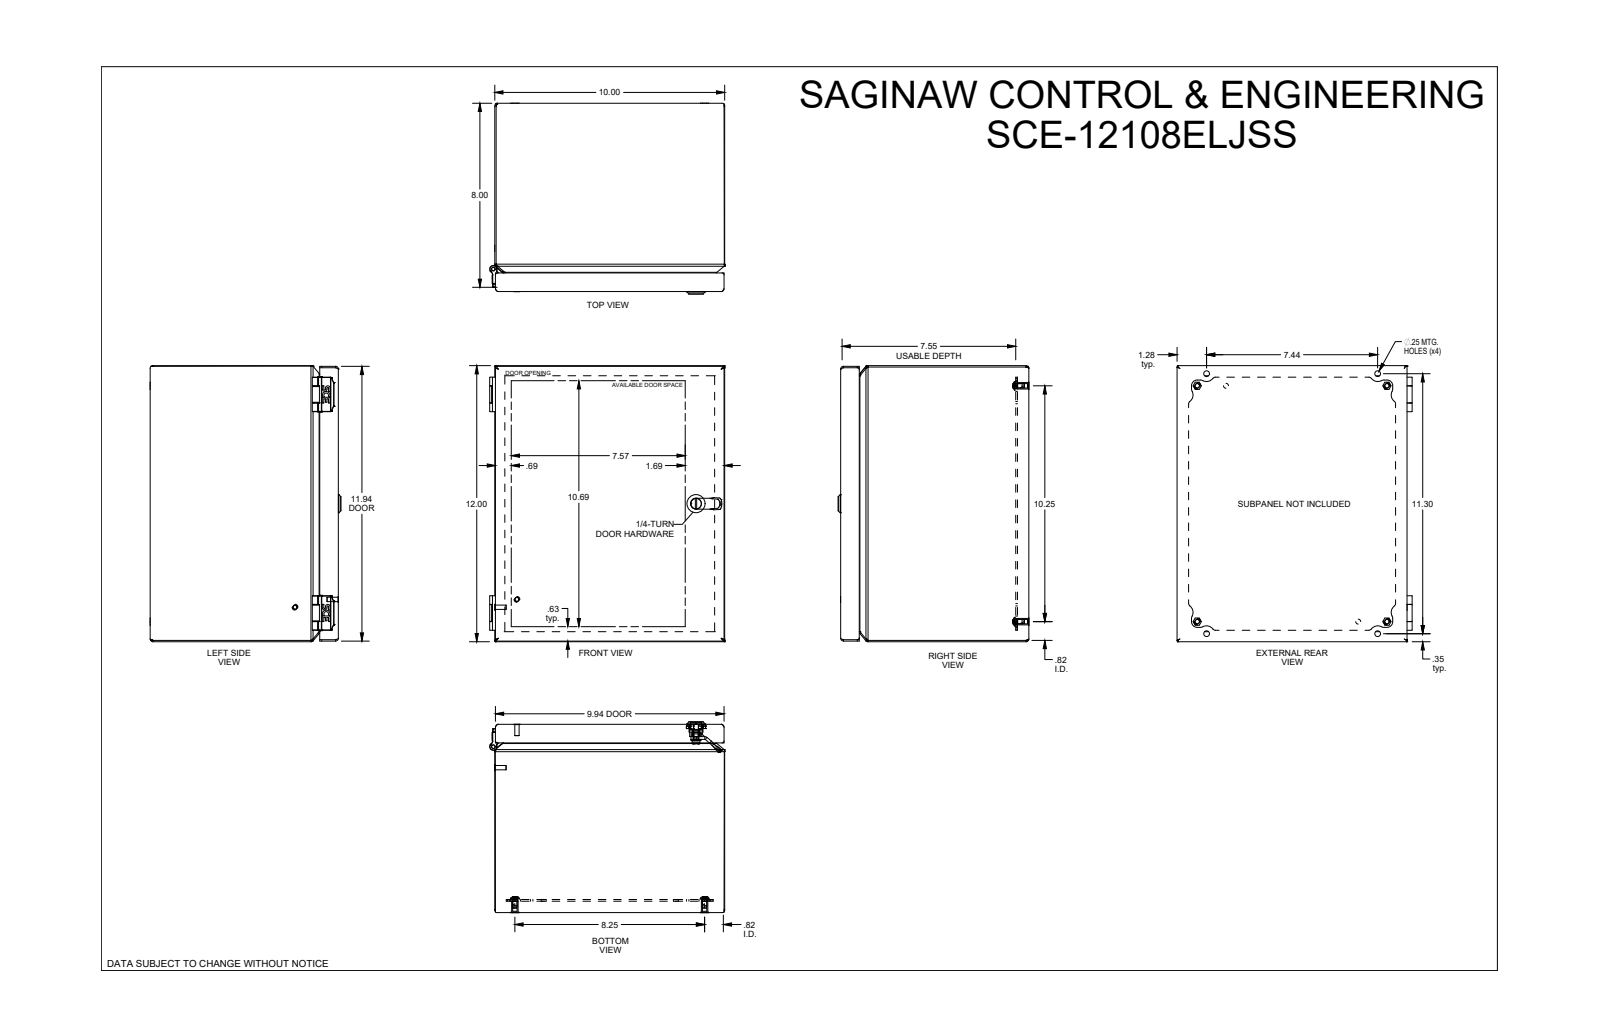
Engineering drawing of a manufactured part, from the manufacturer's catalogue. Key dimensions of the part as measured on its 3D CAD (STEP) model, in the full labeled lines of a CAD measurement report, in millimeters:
Part name (STEP PRODUCT): SCE-12108ELJ
STEP written by: SolidWorks 2019 (AUTOMOTIVE_DESIGN)
Units: millimetres
Bodies: 34 solids, 1079 faces (395 planar, 348 cylindrical, 336 other)
Overall size (bounding box): 306.3 × 259.6 × 210.7
Volume: 789 700 mm³ · Surface area: 985 200 mm²
Round holes (diameter × count): ⌀4.3 ×4, ⌀4.8 ×4, ⌀6.4 ×4, ⌀7.2 ×4, ⌀0.5 ×2, ⌀2.5 ×2, ⌀5.5 ×2, ⌀6.8 ×2, ⌀4 ×1, ⌀5 ×1, ⌀5.1 ×1, ⌀6.1 ×1
Round bosses / shafts (diameter × count): ⌀4.8 ×6, ⌀12.2 ×4, ⌀9.5 ×4, ⌀7.1 ×4, ⌀4.1 ×4, ⌀6.6 ×2, ⌀6.5 ×2, ⌀6 ×2
Partial cylindrical surfaces — rounded edges, fillets, slot ends (radius × count): R0.8 ×28, R0.6 ×24, R0.3 ×21, R1.3 ×16, R6.4 ×13, R3.2 ×11, R0.3 ×10, R1.5 ×10
Main face-to-face distances: 1.5, 254, 1.5, 304.8, 207.9, 206.4, 206.4, 204.9, 14.5, 13
Hole centre spacings: 211.1, 241.3, 1.5, 31.8, 130.5, 177.8, 209.6, 238.7
